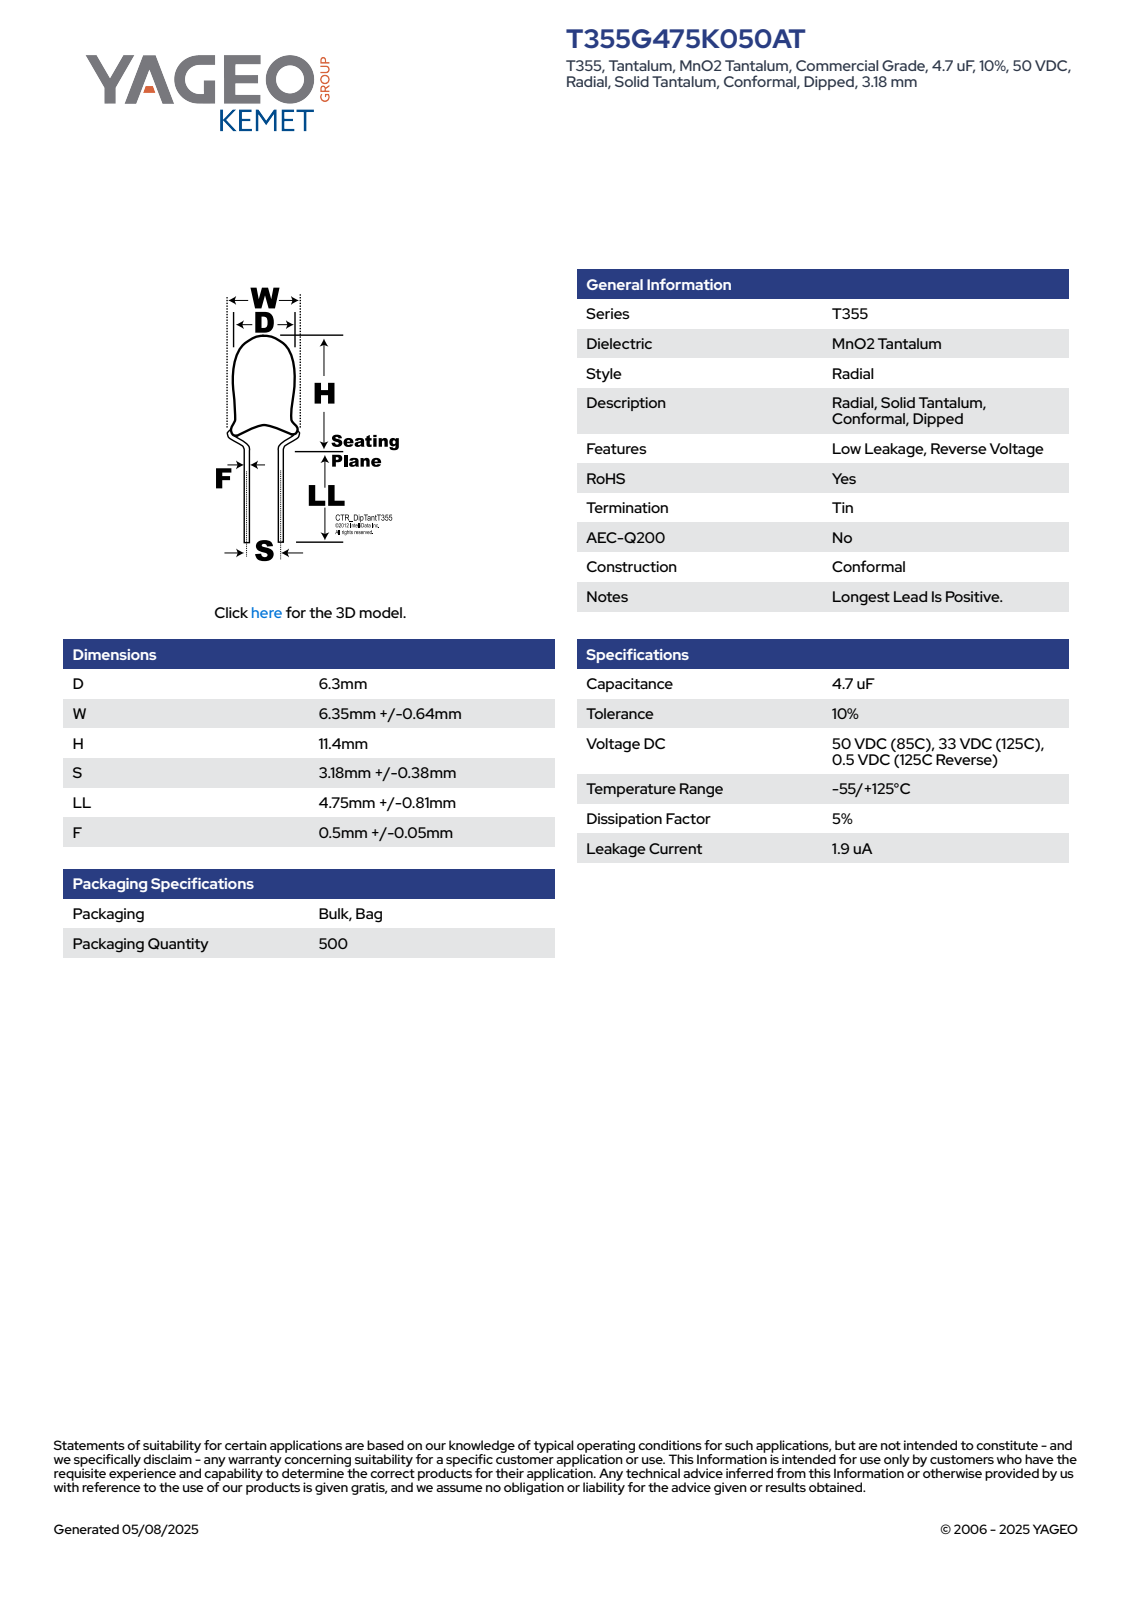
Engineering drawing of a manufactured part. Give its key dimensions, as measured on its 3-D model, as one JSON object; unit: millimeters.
{"part_name": "CTR_T355_D6.3W6.99H11.4S3.18LL5.56F0.55", "step_written_by": "SolidWorks 2021 (AUTOMOTIVE_DESIGN)", "units": "millimeters", "bodies": {"solids": 1, "faces": 100, "planar": 30, "cylindrical": 6, "other": 64}, "overall_size": [16.96, 6.99, 6.3], "volume_mm3": 207, "surface_area_mm2": 213, "round_bosses_or_shafts": [[6.3, 1]], "partial_cylinders_radius": [[3.14, 1]], "face_to_face_distances": [7.95, 9.01, 16.96, 13.39, 4.38, 3.57, 12.79, 3.78, 0.6, 4.17]}
